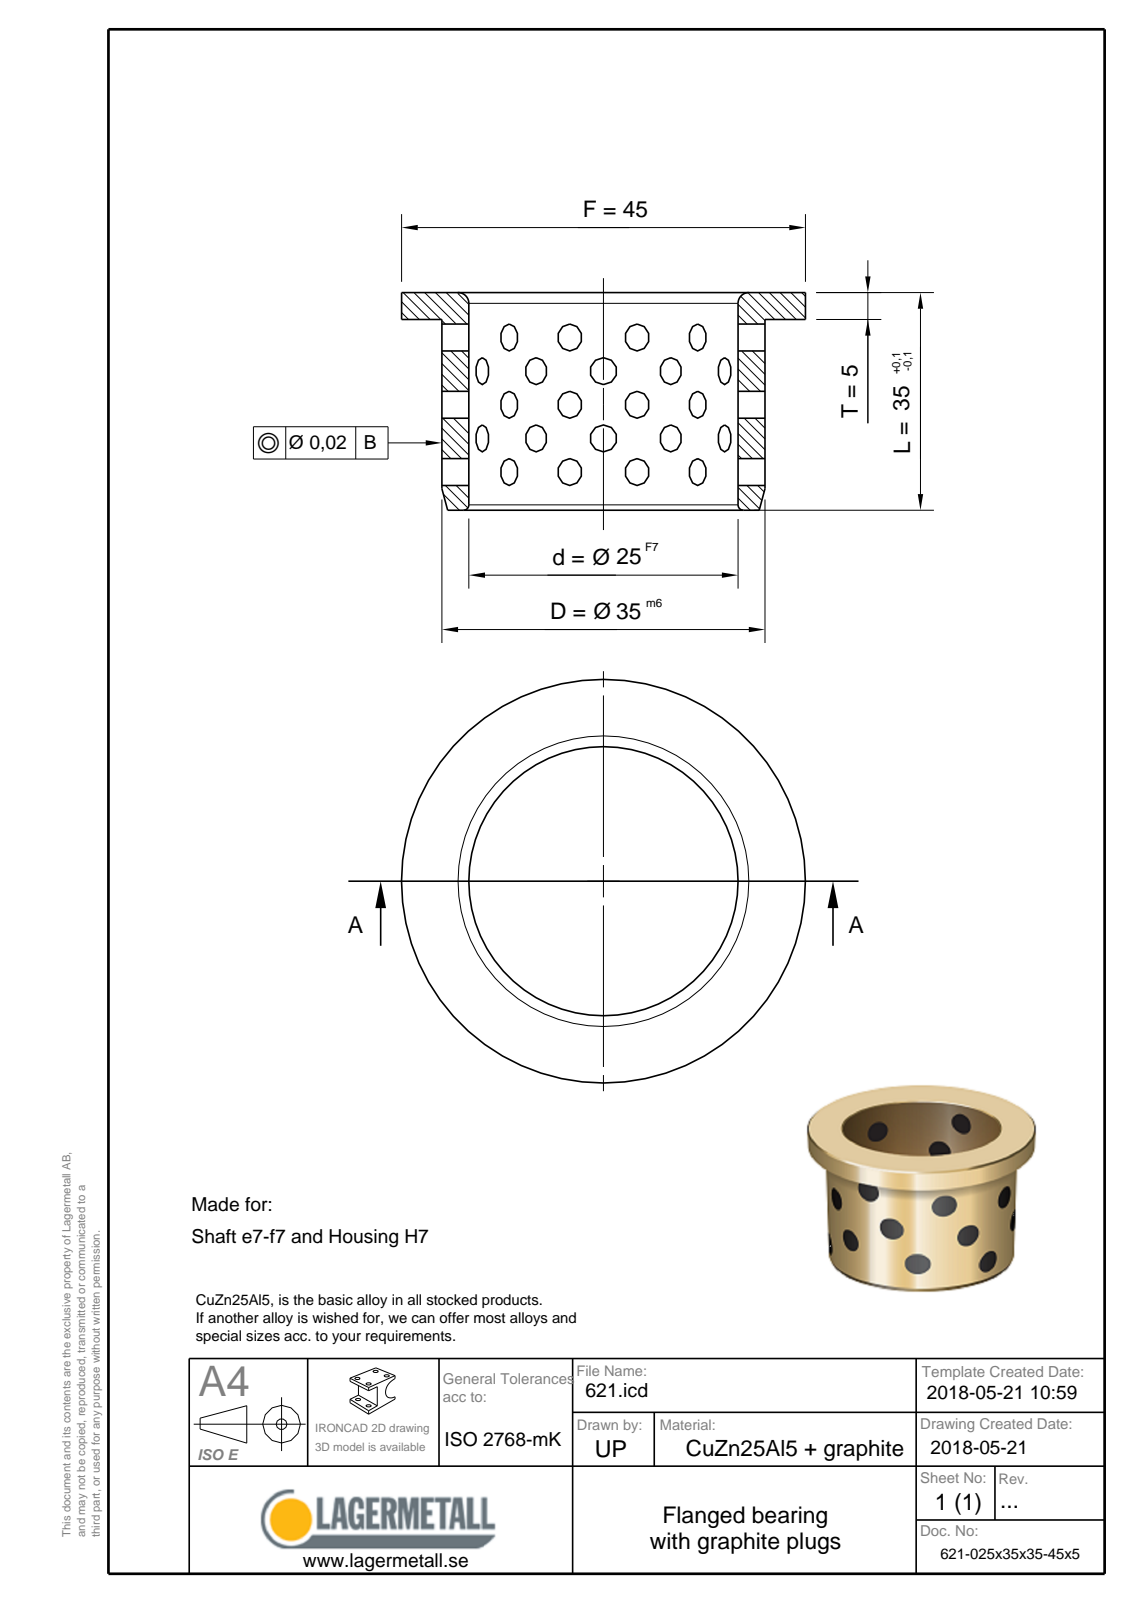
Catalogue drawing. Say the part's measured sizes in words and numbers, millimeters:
The part is named "621-025x35x35-45x5". Its 3-D file was written by "Spatial InterOp 3D (CONFIG_CONTROL_DESIGN)". It is 1 solid with 9 faces: 3 planar, 3 cylindrical and 3 other. Overall it measures 45 by 45 by 35 millimeters. Its volume is 19 458 cubic millimeters and its surface area 8 759 square millimeters. Round holes: 1 of diameter 25. Round bosses or shafts: 1 of diameter 45, 1 of diameter 35. The main face-to-face distances are 5, 30, 35.
